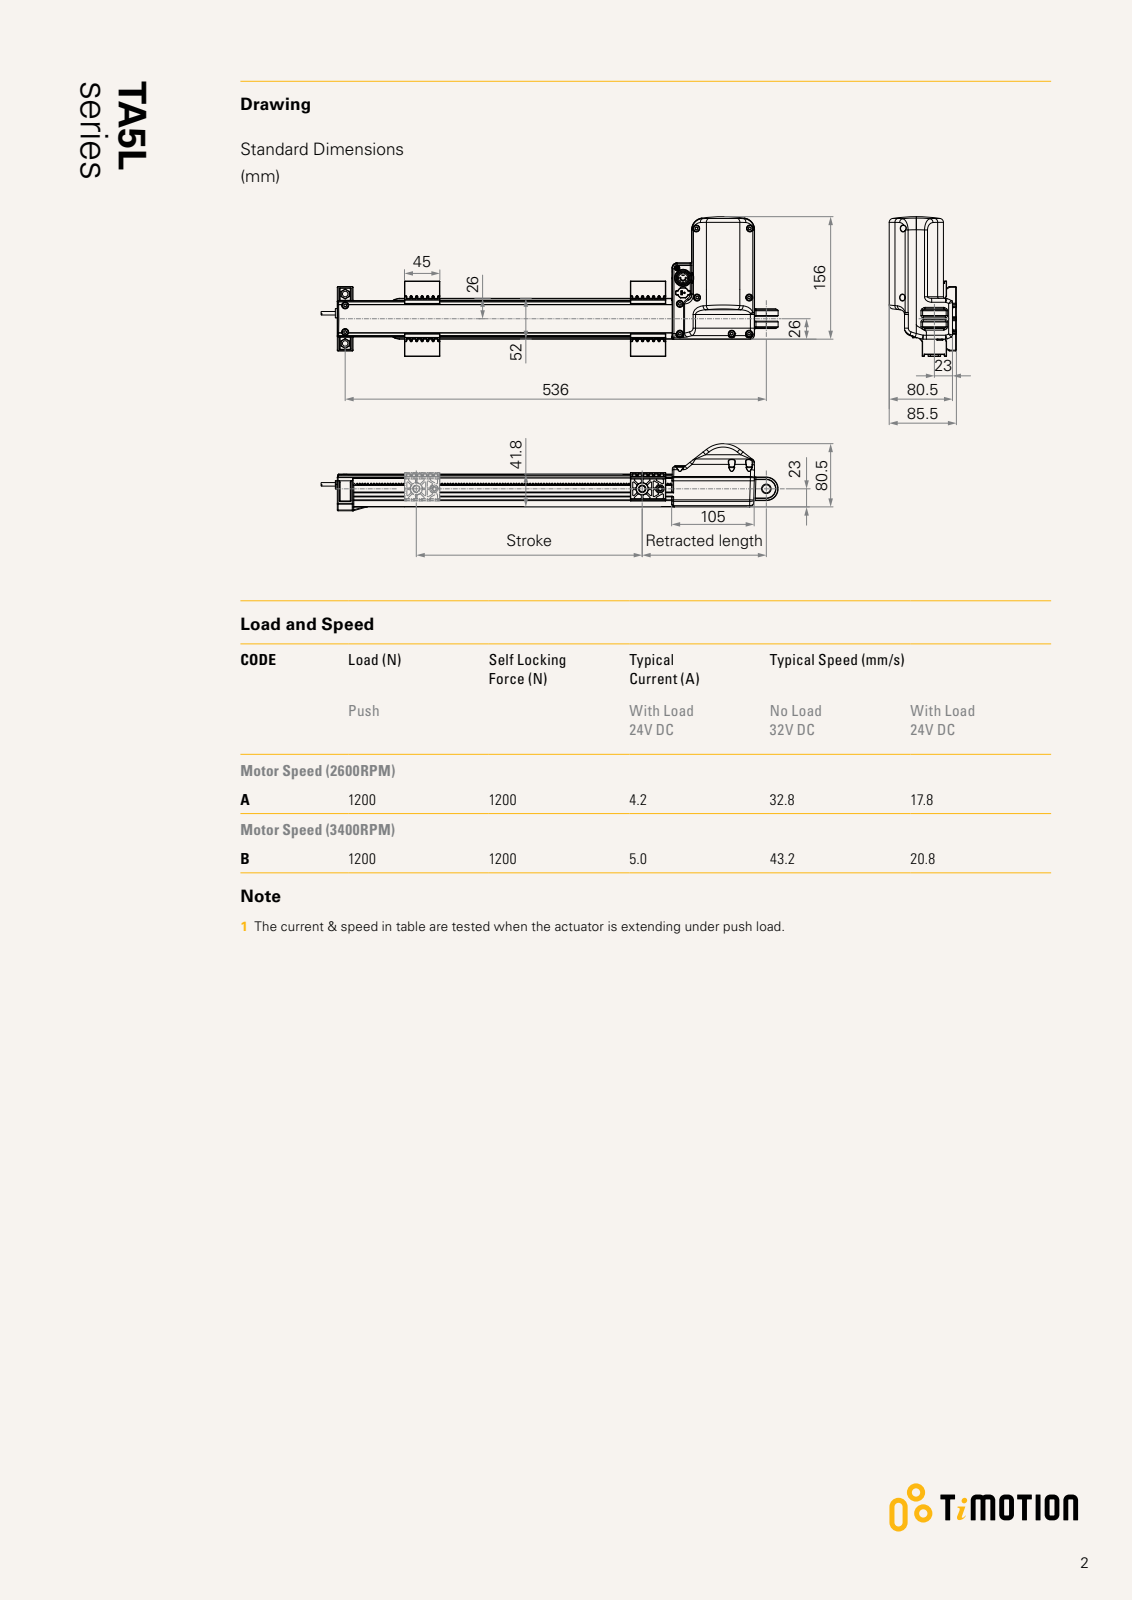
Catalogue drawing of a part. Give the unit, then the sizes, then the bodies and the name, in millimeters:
Units: millimetres
Overall size (bounding box): 561.03 × 178 × 93.1
Round holes (diameter × count): ⌀8 ×4, ⌀4.2 ×2, ⌀7 ×2, ⌀5.3 ×1, ⌀8.5 ×1, ⌀10.2 ×1, ⌀17 ×1
Round bosses / shafts (diameter × count): ⌀7.5 ×6, ⌀4 ×3, ⌀8 ×2, ⌀5 ×2, ⌀21 ×1, ⌀16.4 ×1, ⌀15.9 ×1, ⌀10 ×1
Partial cylindrical surfaces — rounded edges, fillets, slot ends (radius × count): R0.5 ×277, R1 ×107, R0.2 ×60, R2 ×31, R6 ×12, R3 ×10, R5 ×10, R0.8 ×3
Main face-to-face distances: 3, 46, 49, 27.9, 2, 36.1, 8.2, 2.5, 25.5, 22.5
Hole centre spacings: 14.5, 48.5, 426.03, 426.18, 427.55, 428.98, 22, 23
Volume: 1 468 000 mm³ · Surface area: 224 169 mm²
Bodies: 1 solid, 2550 faces (865 planar, 1059 cylindrical, 626 other)
STEP written by: SolidWorks 2010 (AUTOMOTIVE_DESIGN)
